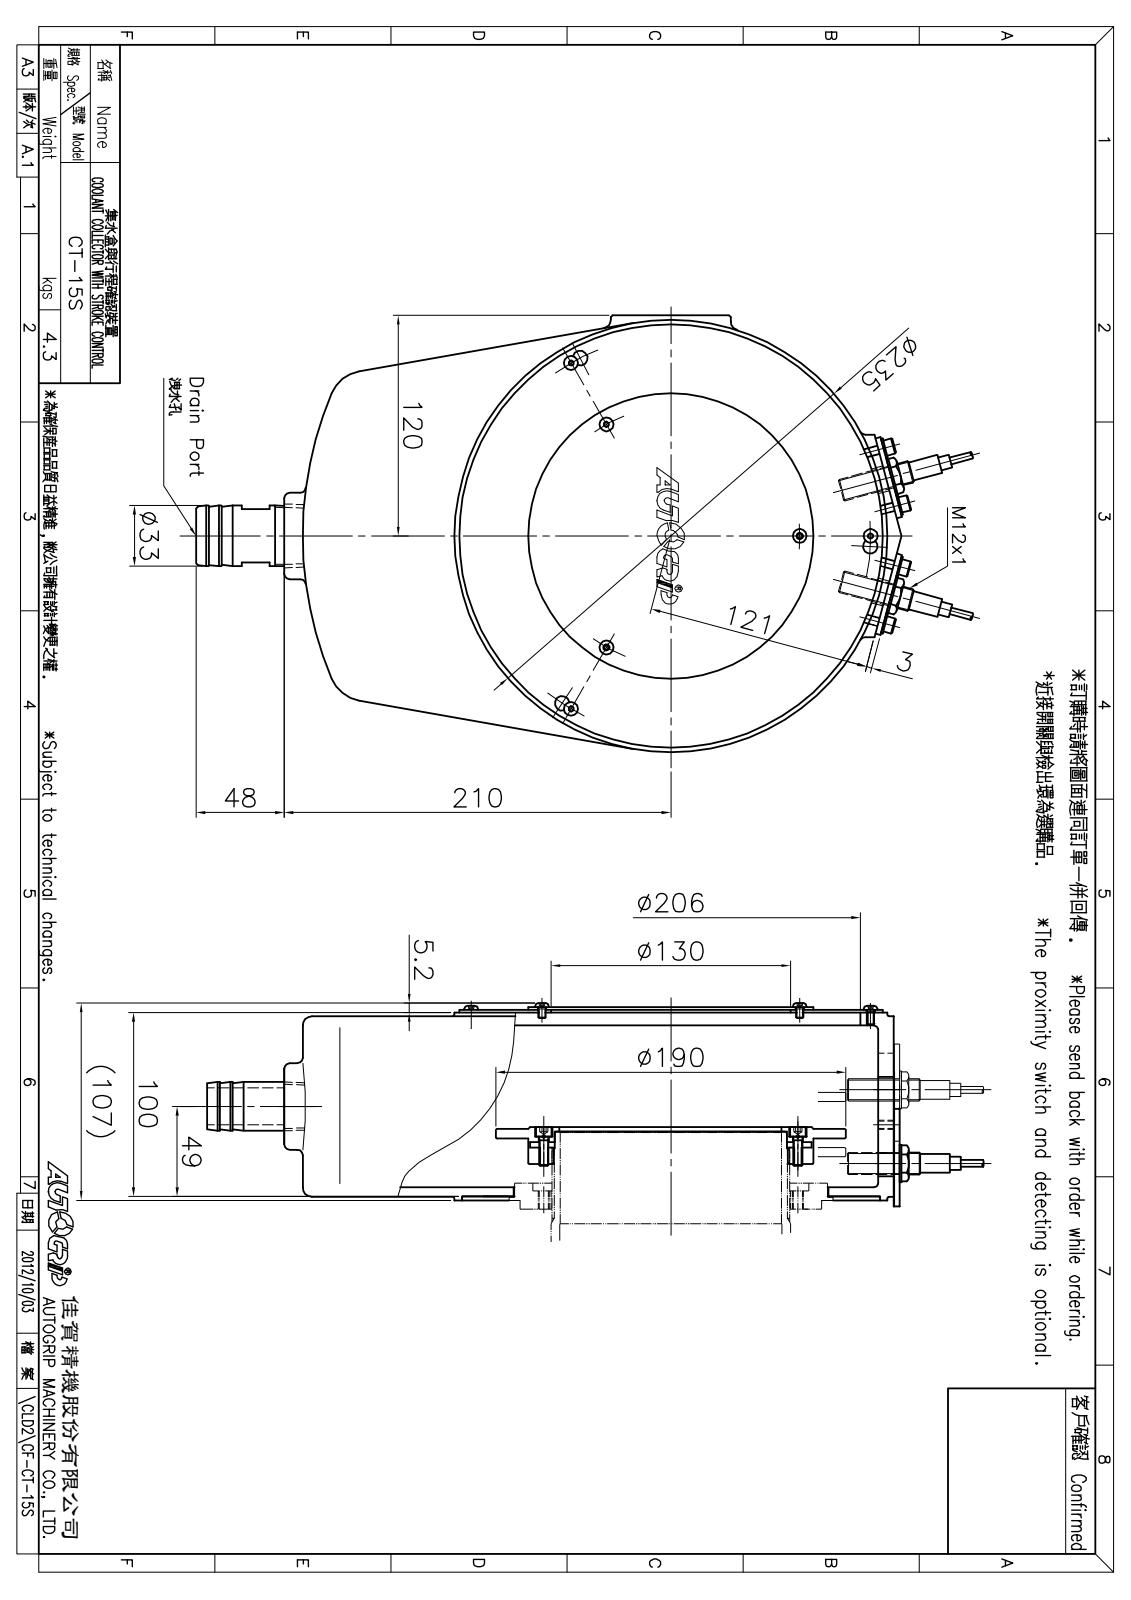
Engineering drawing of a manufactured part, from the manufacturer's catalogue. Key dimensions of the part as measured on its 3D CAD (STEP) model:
Part name (STEP PRODUCT): CF-CT-15S; CT-08洩油管; M5x10; CF-CT-15集水盒本體 (+3 more)
STEP written by: SolidWorks 2016 (CONFIG_CONTROL_DESIGN)
Units: millimetres
Bodies: 25 solids, 661 faces (302 planar, 211 cylindrical, 148 other)
Overall size (bounding box): 424.56 × 237.5 × 107
Volume: 1 085 000 mm³ · Surface area: 500 440 mm²
Round holes (diameter × count): ⌀4 ×6, ⌀5 ×6, ⌀5.5 ×4, ⌀7 ×4, ⌀4.6 ×3, ⌀9.5 ×2, ⌀12 ×2, ⌀25 ×1, ⌀120.5 ×1, ⌀126 ×1, ⌀129 ×1, ⌀130 ×1
Round bosses / shafts (diameter × count): ⌀8.5 ×6, ⌀7 ×6, ⌀12 ×2, ⌀11 ×2, ⌀10.2 ×2, ⌀7.2 ×2, ⌀3.7 ×2, ⌀235 ×1
Partial cylindrical surfaces — rounded edges, fillets, slot ends (radius × count): R2.75 ×16, R2 ×10, R7 ×8, R5 ×6, R3 ×4, R15 ×2, R20 ×2, R112.5 ×1
Main face-to-face distances: 5, 1.5, 98, 95, 93, 96.5, 7, 2, 3, 10
Hole centre spacings: 74.44, 105.01, 148.5, 155.78, 161.35, 38.5, 70, 108.5
